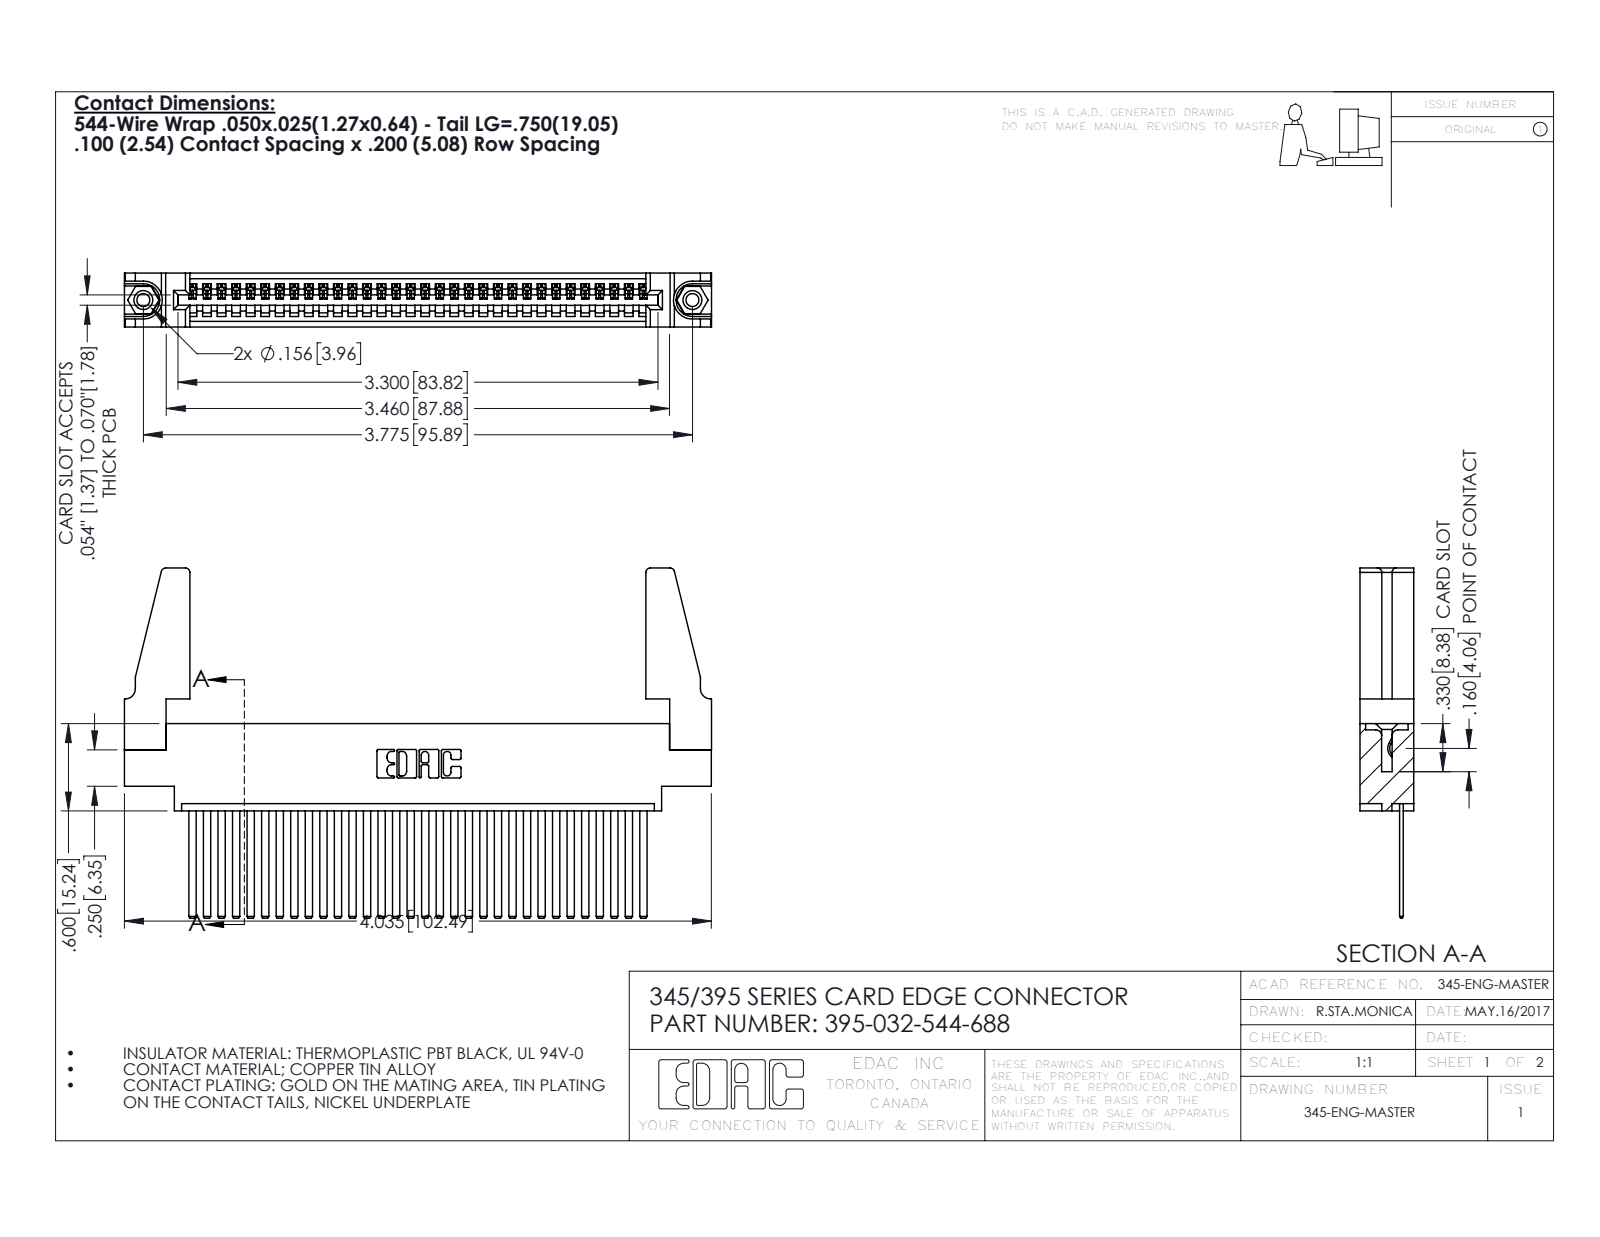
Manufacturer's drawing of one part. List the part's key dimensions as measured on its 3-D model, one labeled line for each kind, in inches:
Part name (STEP PRODUCT): 345-220-078_345-220-088; 345-292-001_345-293-144; 395-032-544-688; 345 Part_0.170 Offset - 0.156 Dia-TH (+1 more)
STEP written by: SolidWorks 2016 (CONFIG_CONTROL_DESIGN)
Units: inches
Bodies: 37 solids, 1918 faces (1308 planar, 594 cylindrical, 16 other)
Overall size (bounding box): 4.036 × 2.407 × 0.37
Volume: 0.803 in³ · Surface area: 26.98 in²
Round holes (diameter × count): ⌀0.089 ×2, ⌀0.125 ×2, ⌀0.156 ×2, ⌀0.064 ×1
Round bosses / shafts (diameter × count): ⌀0.155 ×2
Partial cylindrical surfaces — rounded edges, fillets, slot ends (radius × count): R0.006 ×64, R0.01 ×22, R0.03 ×8, R0.007 ×6, R0.031 ×6, R0.026 ×3, R0.031 ×2, R0.04 ×2
Main face-to-face distances: 0.072, 0.298, 0.37, 0.098, 0.272, 0.025, 0.2, 0.225, 0.175, 0.149
Hole centre spacings: 0.27, 3.54, 3.775
